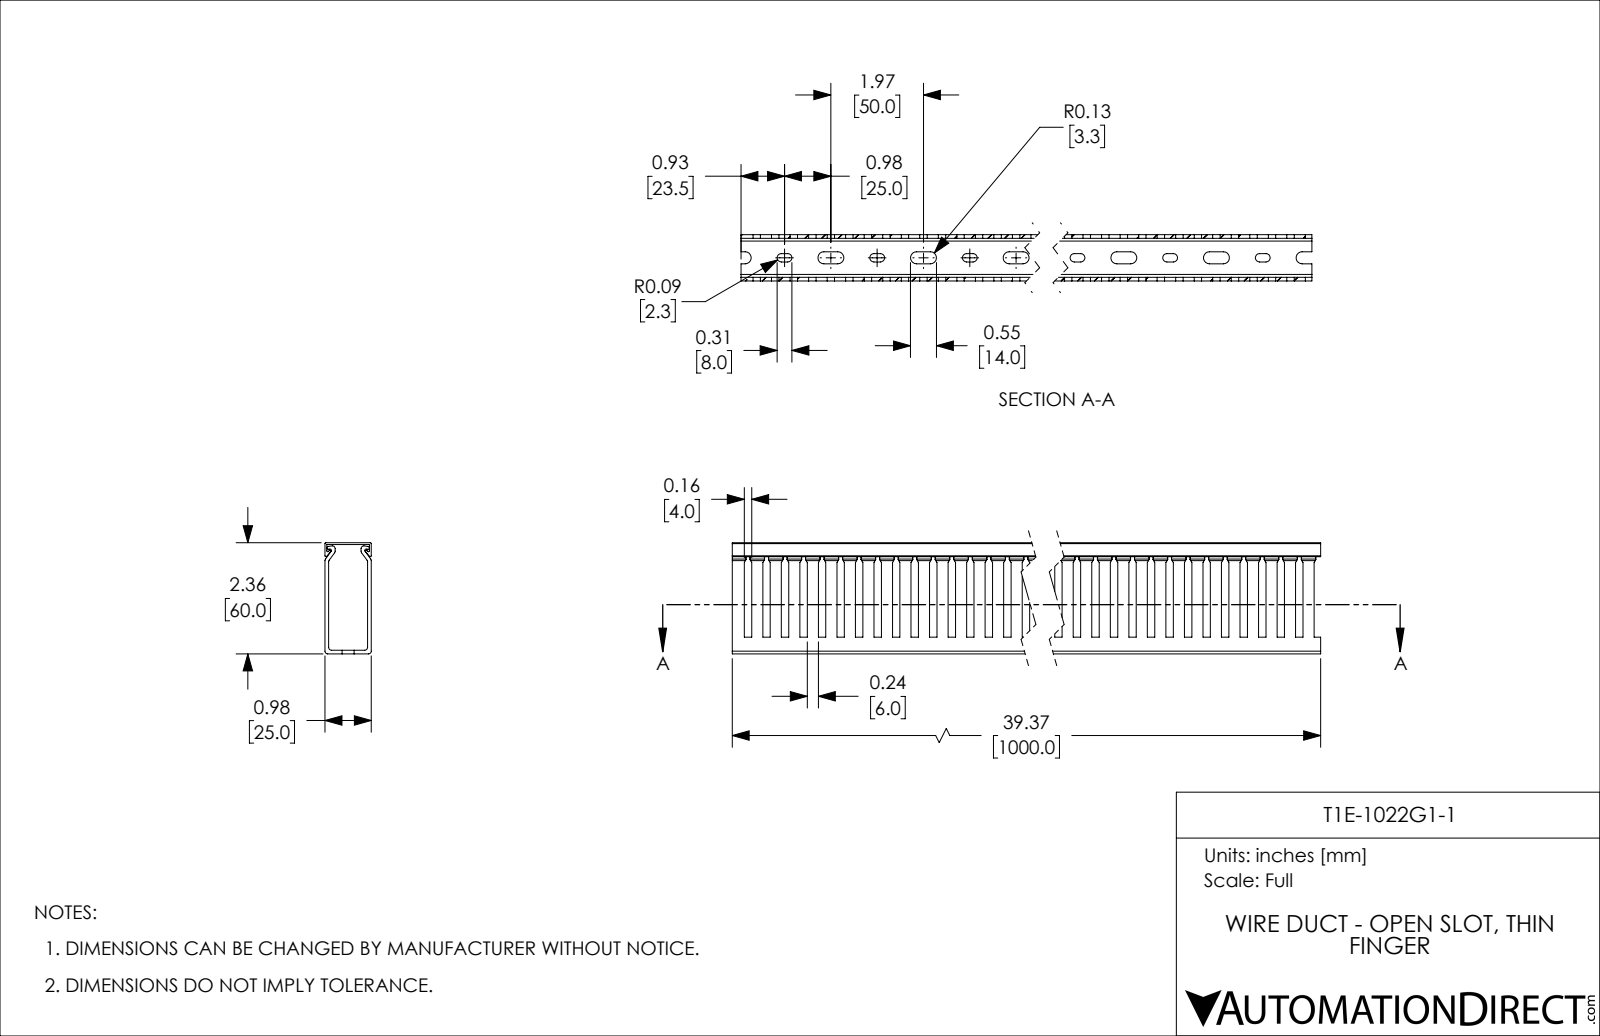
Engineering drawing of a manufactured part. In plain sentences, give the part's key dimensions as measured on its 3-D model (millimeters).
The part is named "T1E-1022G1-1". Its 3-D file was written by "SolidWorks 2021 (CONFIG_CONTROL_DESIGN)". It is 2 solids with 745 faces: 434 planar, 311 cylindrical and 0 other. Overall it measures 1000 by 60 by 25 millimeters. Its volume is 317 763 cubic millimeters and its surface area 366 051 square millimeters. Partial cylindrical surfaces (rounded edges, fillets, slot ends): 40 of radius 2.25, 40 of radius 3.25, 12 of radius 1.5, 8 of radius 0.5, 6 of radius 0.75. The main face-to-face distances are 2, 23, 25, 21, 1, 60, 59, 57, 58, 24.
